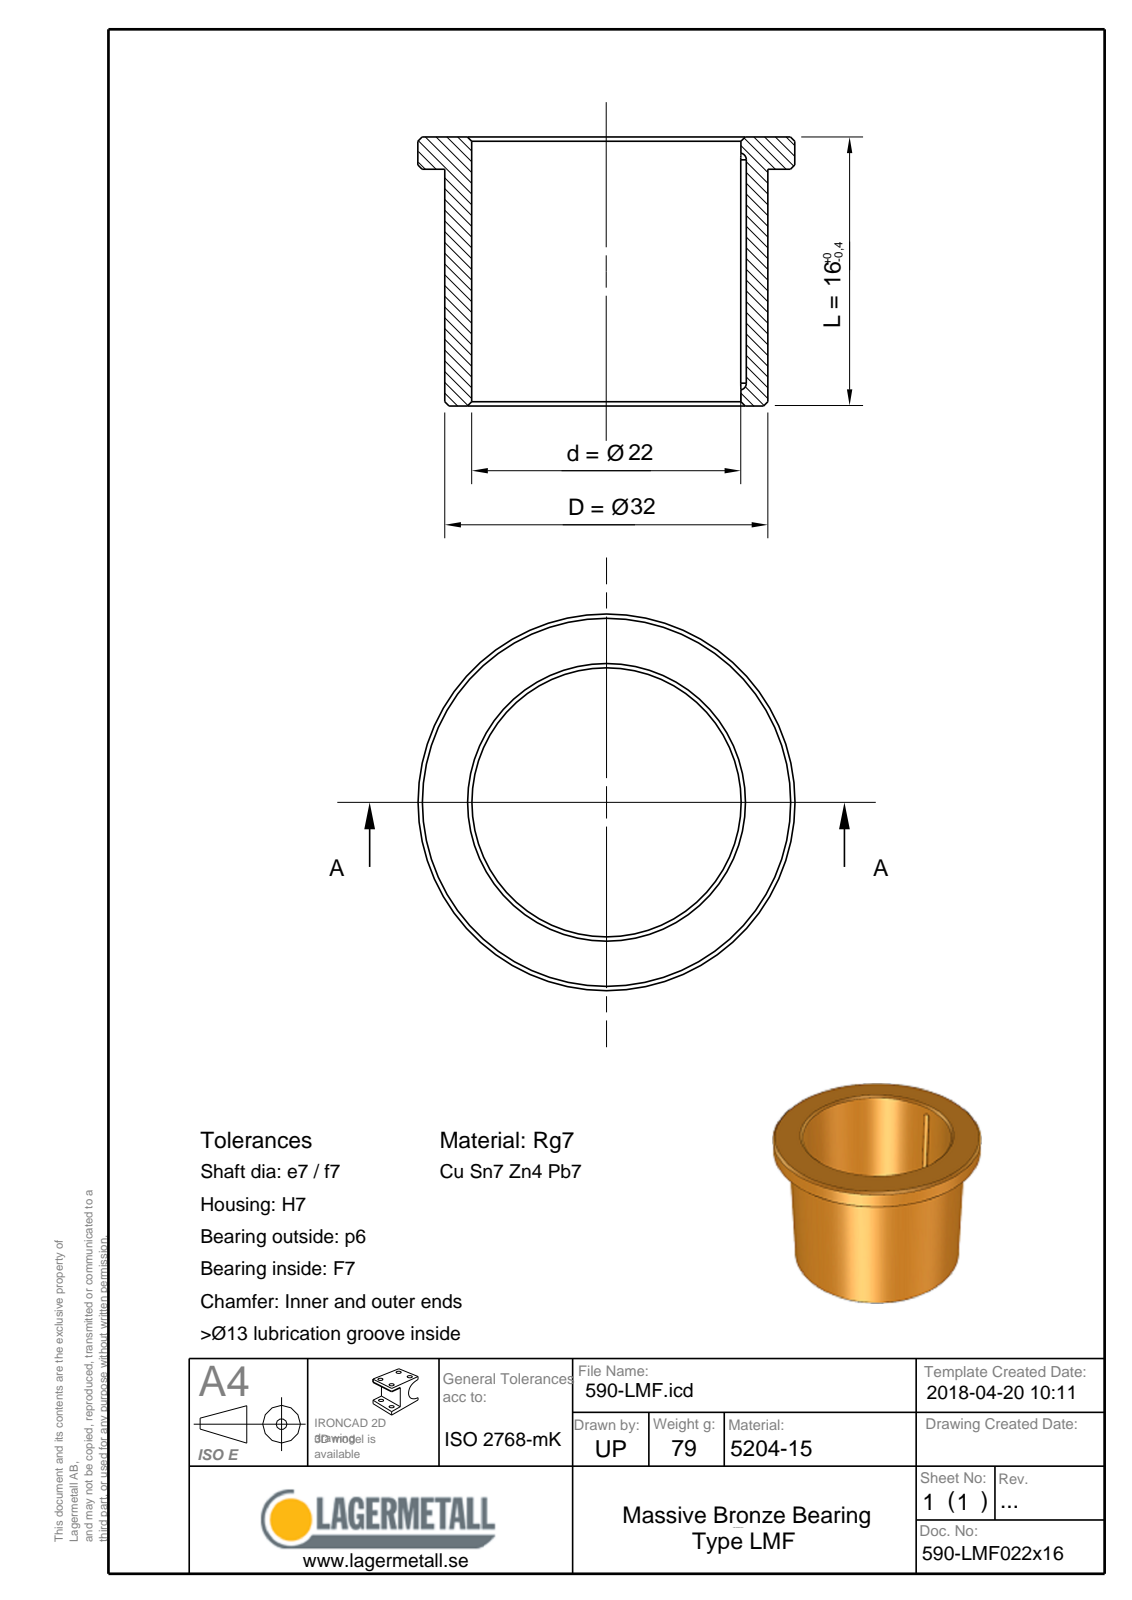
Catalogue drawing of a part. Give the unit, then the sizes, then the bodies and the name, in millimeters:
Units: millimetres
Overall size (bounding box): 40 × 40 × 16
Round holes (diameter × count): ⌀22 ×1
Round bosses / shafts (diameter × count): ⌀40 ×1, ⌀32 ×1
Partial cylindrical surfaces — rounded edges, fillets, slot ends (radius × count): R0.75 ×3
Main face-to-face distances: 5, 11, 16, 1.5
Volume: 8 975 mm³ · Surface area: 4 464 mm²
Bodies: 1 solid, 18 faces (5 planar, 6 cylindrical, 7 other)
Part name (STEP PRODUCT): 590-LMF022x16
STEP written by: Spatial InterOp 3D (CONFIG_CONTROL_DESIGN)
